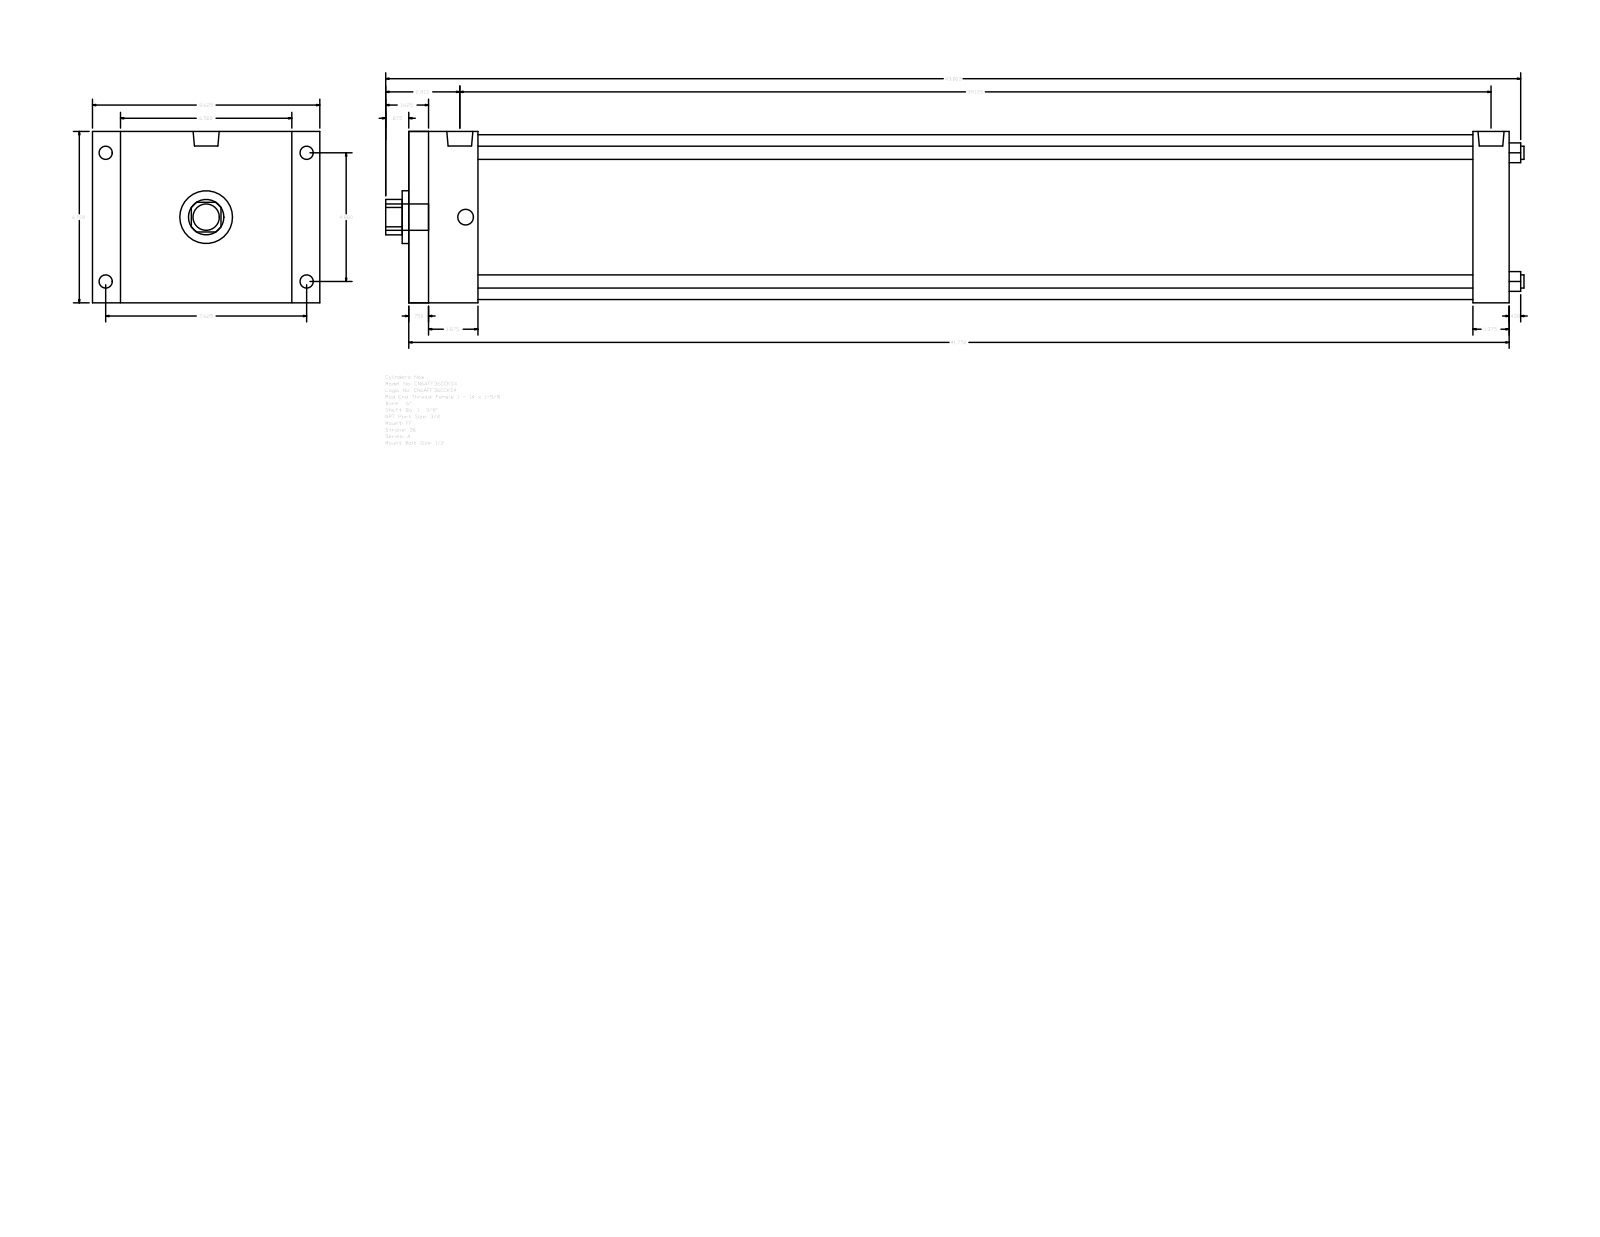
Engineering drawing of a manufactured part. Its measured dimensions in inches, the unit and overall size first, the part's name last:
Units: inches
Overall size (bounding box): 43.187 × 8.625 × 6.5
Round holes (diameter × count): ⌀0.5 ×4, ⌀1.375 ×1, ⌀2 ×1, ⌀6.25 ×1
Round bosses / shafts (diameter × count): ⌀0.594 ×4, ⌀0.5 ×4, ⌀0.989 ×2, ⌀1 ×1
Partial cylindrical surfaces — rounded edges, fillets, slot ends (radius × count): R0.672 ×1
Main face-to-face distances: 6.5, 41.75, 0.75, 41, 2.625, 1.875, 39.125, 40.375, 39.625, 37.75
Hole centre spacings: 3.451, 4.88, 6.902
Bodies: 0 solids, 92 faces (64 planar, 28 cylindrical, 0 other)
Part name (STEP PRODUCT): A_FF__0600_1.375
STEP written by: GSSL Pune (CONFIG_CONTROL_DESIGN)
